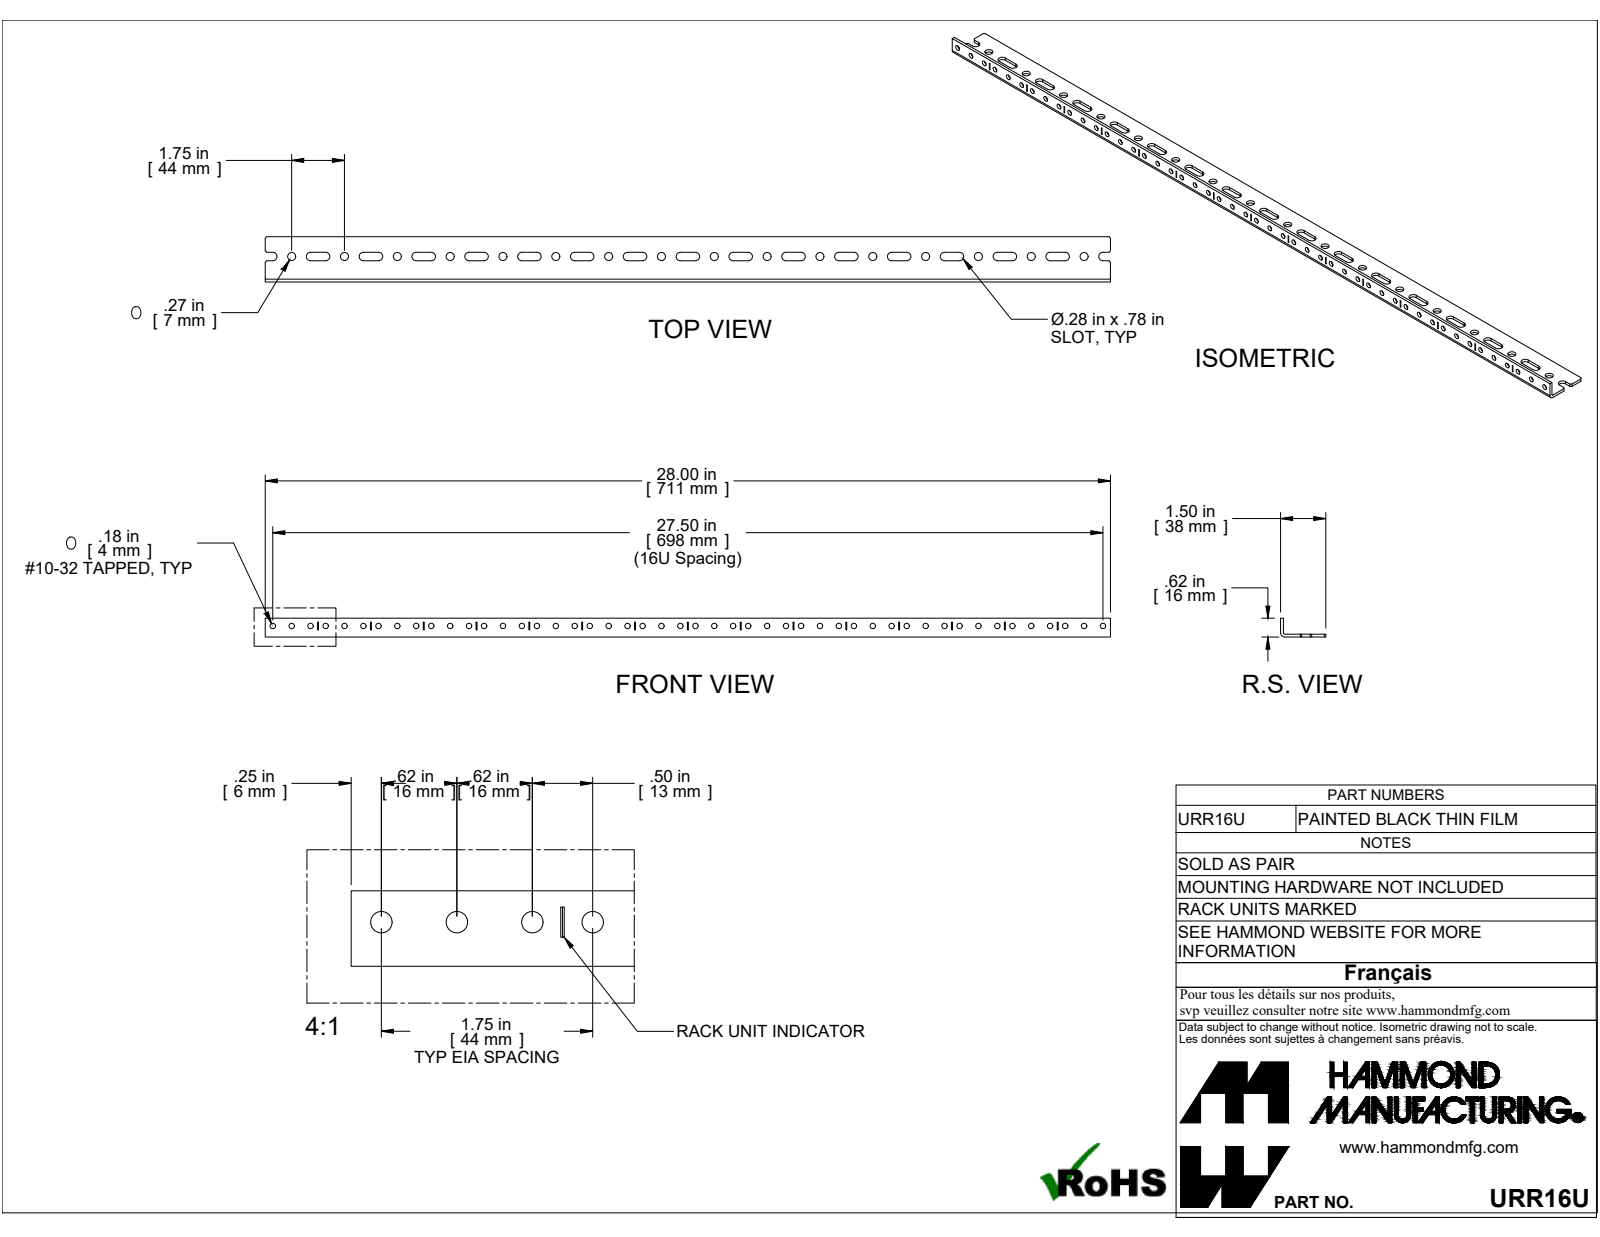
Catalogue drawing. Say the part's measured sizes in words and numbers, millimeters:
The part is named "COM57213-16". Its 3-D file was written by "ST-DEVELOPER v16.7 (AUTOMOTIVE_DESIGN)". It is 1 solid with 208 faces: 110 planar, 98 cylindrical and 0 other. Overall it measures 711.2 by 38.1 by 15.88 millimeters. Its volume is 78 399 cubic millimeters and its surface area 73 008 square millimeters. Round holes: 48 of diameter 4.5, 16 of diameter 6.76. Partial cylindrical surfaces (rounded edges, fillets, slot ends): 32 of radius 3.57, 1 of radius 1.22, 1 of radius 3.63. The main face-to-face distances are 2.41, 15.88, 13.47, 38.1, 35.69, 17.84, 24.98, 15.43, 22.57, 7.14. The hole center spacings are 88.9, 44.45, 133.35, 177.8, 266.7, 311.15, 15.87, 15.88.
